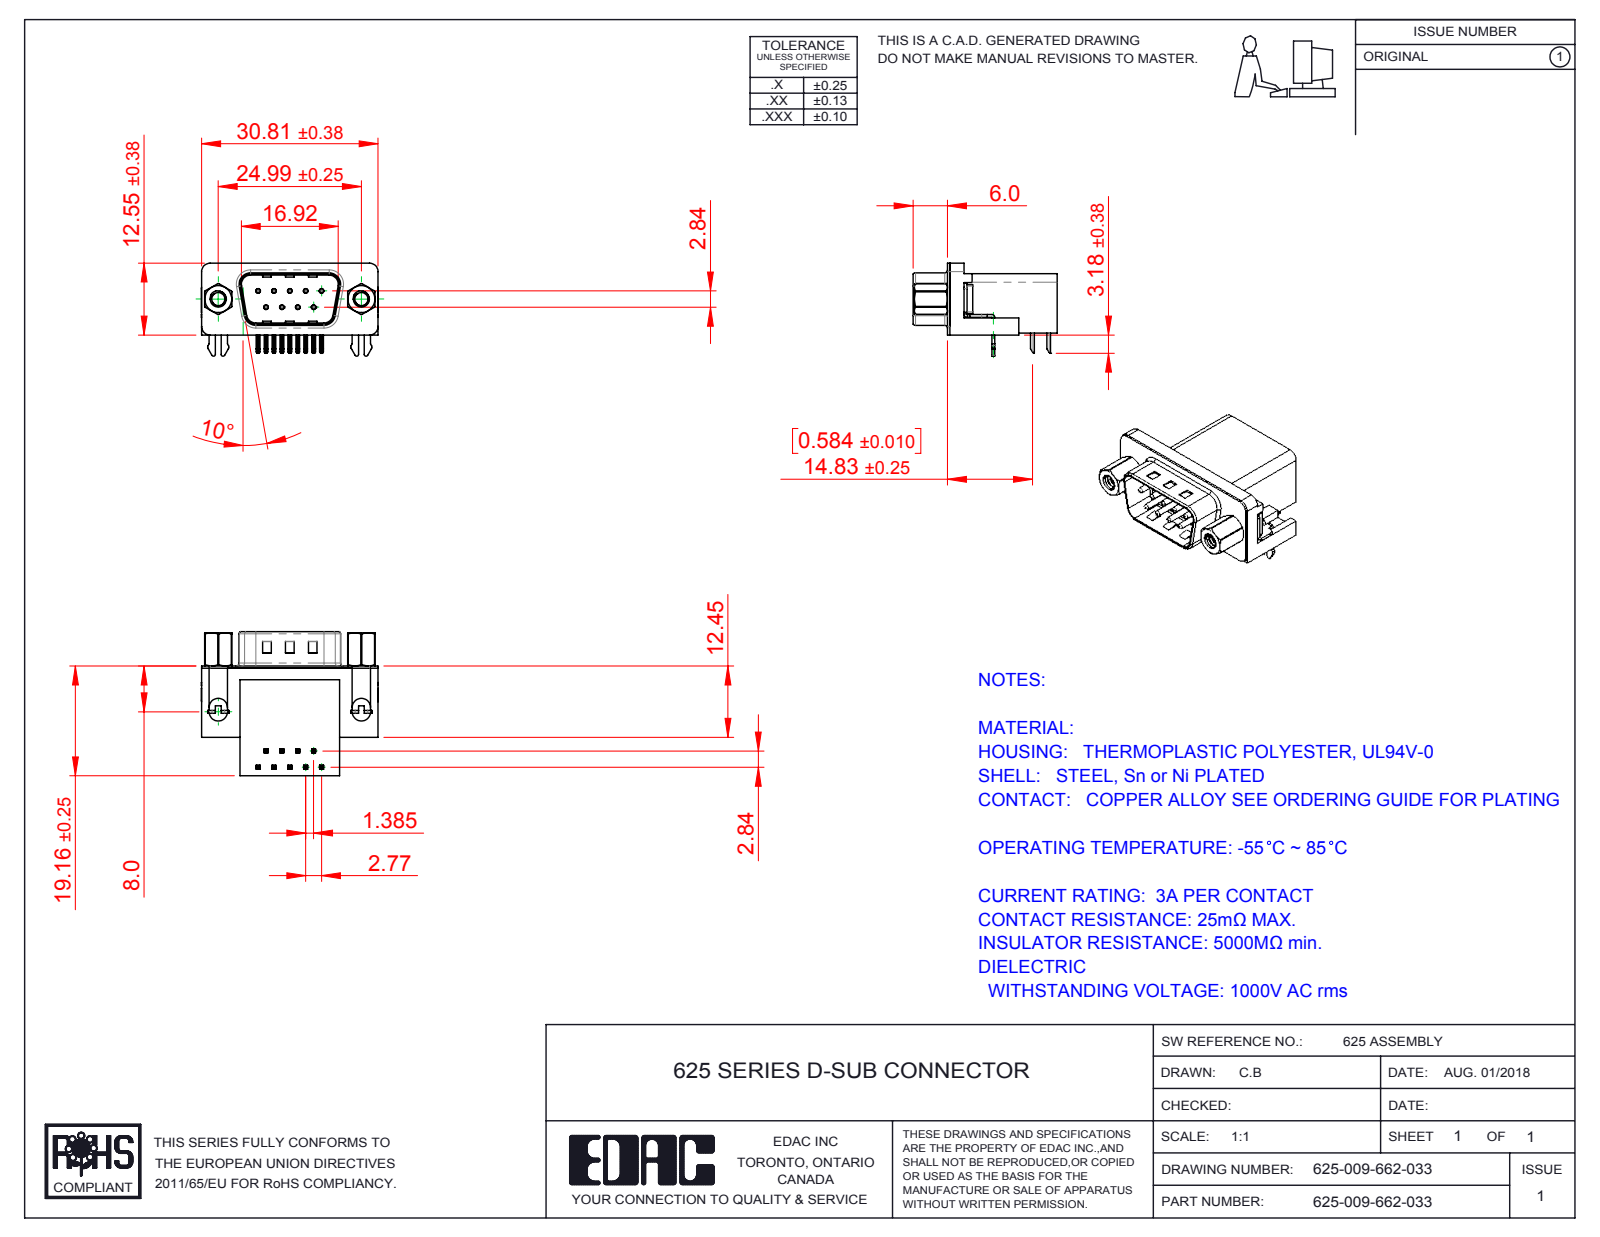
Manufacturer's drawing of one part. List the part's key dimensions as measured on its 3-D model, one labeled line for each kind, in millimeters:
Part name (STEP PRODUCT): 625 Contact Top; 625 Shell_9 Socket; 625 2 Prong Board Lock; 625 4-40 Threaded Rivet (+4 more)
STEP written by: SolidWorks 2016 (CONFIG_CONTROL_DESIGN)
Units: millimetres
Bodies: 17 solids, 1159 faces (627 planar, 397 cylindrical, 135 other)
Overall size (bounding box): 30.89 × 25.16 × 16.25
Volume: 4 688 mm³ · Surface area: 5 440 mm²
Round holes (diameter × count): ⌀0.35 ×9, ⌀0.8 ×9, ⌀2.26 ×2, ⌀2.29 ×2, ⌀4 ×2, ⌀4.8 ×2, ⌀5 ×2
Round bosses / shafts (diameter × count): ⌀0.75 ×9, ⌀4.9 ×2, ⌀4.75 ×2, ⌀3.9 ×2, ⌀2.79 ×2
Partial cylindrical surfaces — rounded edges, fillets, slot ends (radius × count): R0.25 ×44, R0.12 ×18, R1 ×16, R0.5 ×14, R1.5 ×8, R1.6 ×8, R0.32 ×4, R0.9 ×4
Main face-to-face distances: 0.4, 10.34, 18.76, 19.16, 16.26, 2.5, 2.9, 0.35, 10.69, 0.5
Hole centre spacings: 3.16, 2.77, 5.54, 5.03, 5.04, 8.31, 7.48, 7.49
